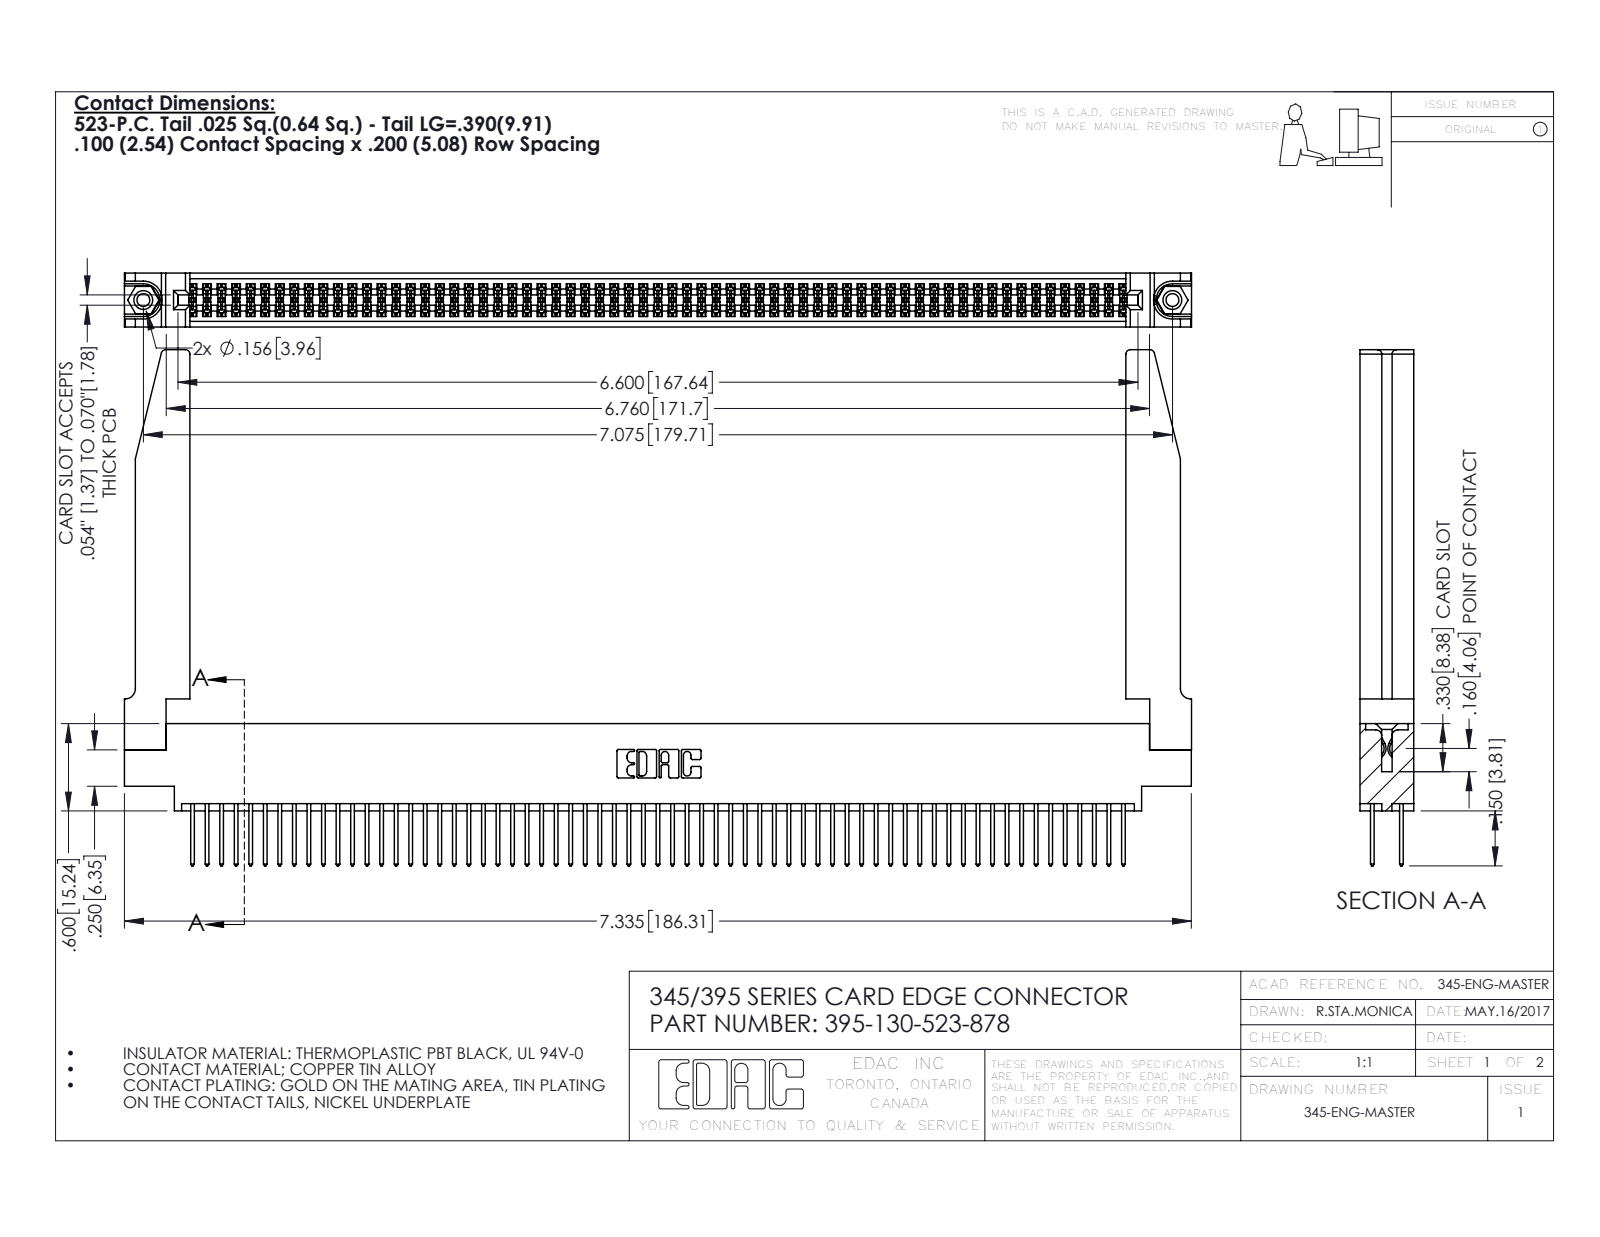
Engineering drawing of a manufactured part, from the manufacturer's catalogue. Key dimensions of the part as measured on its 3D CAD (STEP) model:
Part name (STEP PRODUCT): 345-220-078_345-220-078; 395-130-523-878; 345-292-001_345-293-123; 345-250-001_345-250-001-102 (+1 more)
STEP written by: SolidWorks 2016 (CONFIG_CONTROL_DESIGN)
Units: inches
Bodies: 135 solids, 6864 faces (4516 planar, 2296 cylindrical, 52 other)
Overall size (bounding box): 7.336 × 3.547 × 0.37
Volume: 1.601 in³ · Surface area: 55.68 in²
Round holes (diameter × count): ⌀0.089 ×2, ⌀0.125 ×2, ⌀0.156 ×2, ⌀0.064 ×1
Round bosses / shafts (diameter × count): ⌀0.155 ×2
Partial cylindrical surfaces — rounded edges, fillets, slot ends (radius × count): R0.006 ×195, R0.01 ×130, R0.01 ×22, R0.03 ×8, R0.007 ×6, R0.031 ×6, R0.026 ×3, R0.014 ×2
Main face-to-face distances: 0.072, 0.298, 0.37, 0.098, 0.272, 0.025, 0.2, 0.225, 0.175, 0.148
Hole centre spacings: 0.27, 6.839, 7.075
